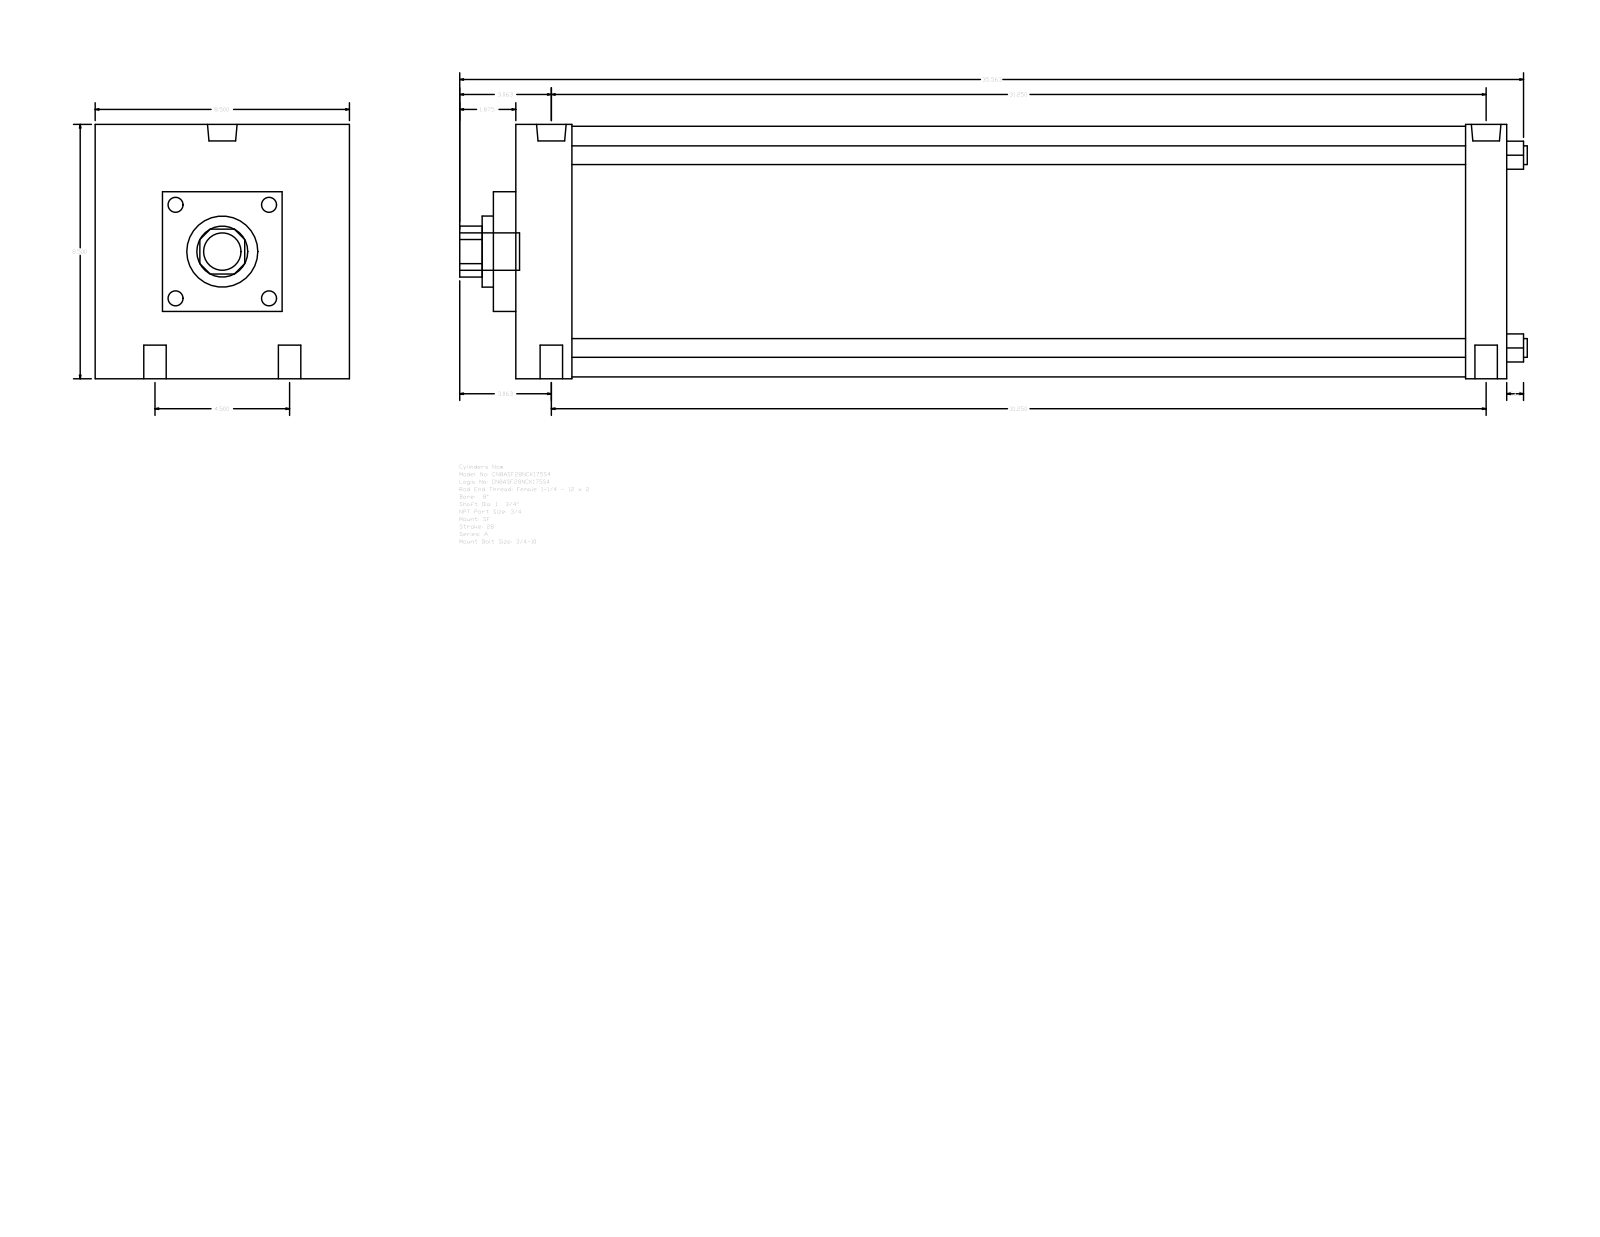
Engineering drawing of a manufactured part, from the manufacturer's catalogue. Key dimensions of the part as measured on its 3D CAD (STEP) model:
Part name (STEP PRODUCT): A_SF__0800_1.75
STEP written by: GSSL Pune (CONFIG_CONTROL_DESIGN)
Units: millimetres
Bodies: 0 solids, 93 faces (67 planar, 26 cylindrical, 0 other)
Overall size (bounding box): 906.46 × 215.9 × 215.9
Round holes (diameter × count): ⌀19.05 ×4, ⌀15.08 ×2, ⌀25.12 ×2, ⌀44.45 ×1, ⌀60.33 ×1
Round bosses / shafts (diameter × count): ⌀15.88 ×4, ⌀212.72 ×1, ⌀31.75 ×1
Partial cylindrical surfaces — rounded edges, fillets, slot ends (radius × count): R21.63 ×1
Main face-to-face distances: 841.38, 215.9, 34.92, 47.63, 806.46, 758.83, 793.75, 19.05, 158.75, 57.15
Hole centre spacings: 57.15, 795.8, 793.75, 114.3, 801.94, 781.05
